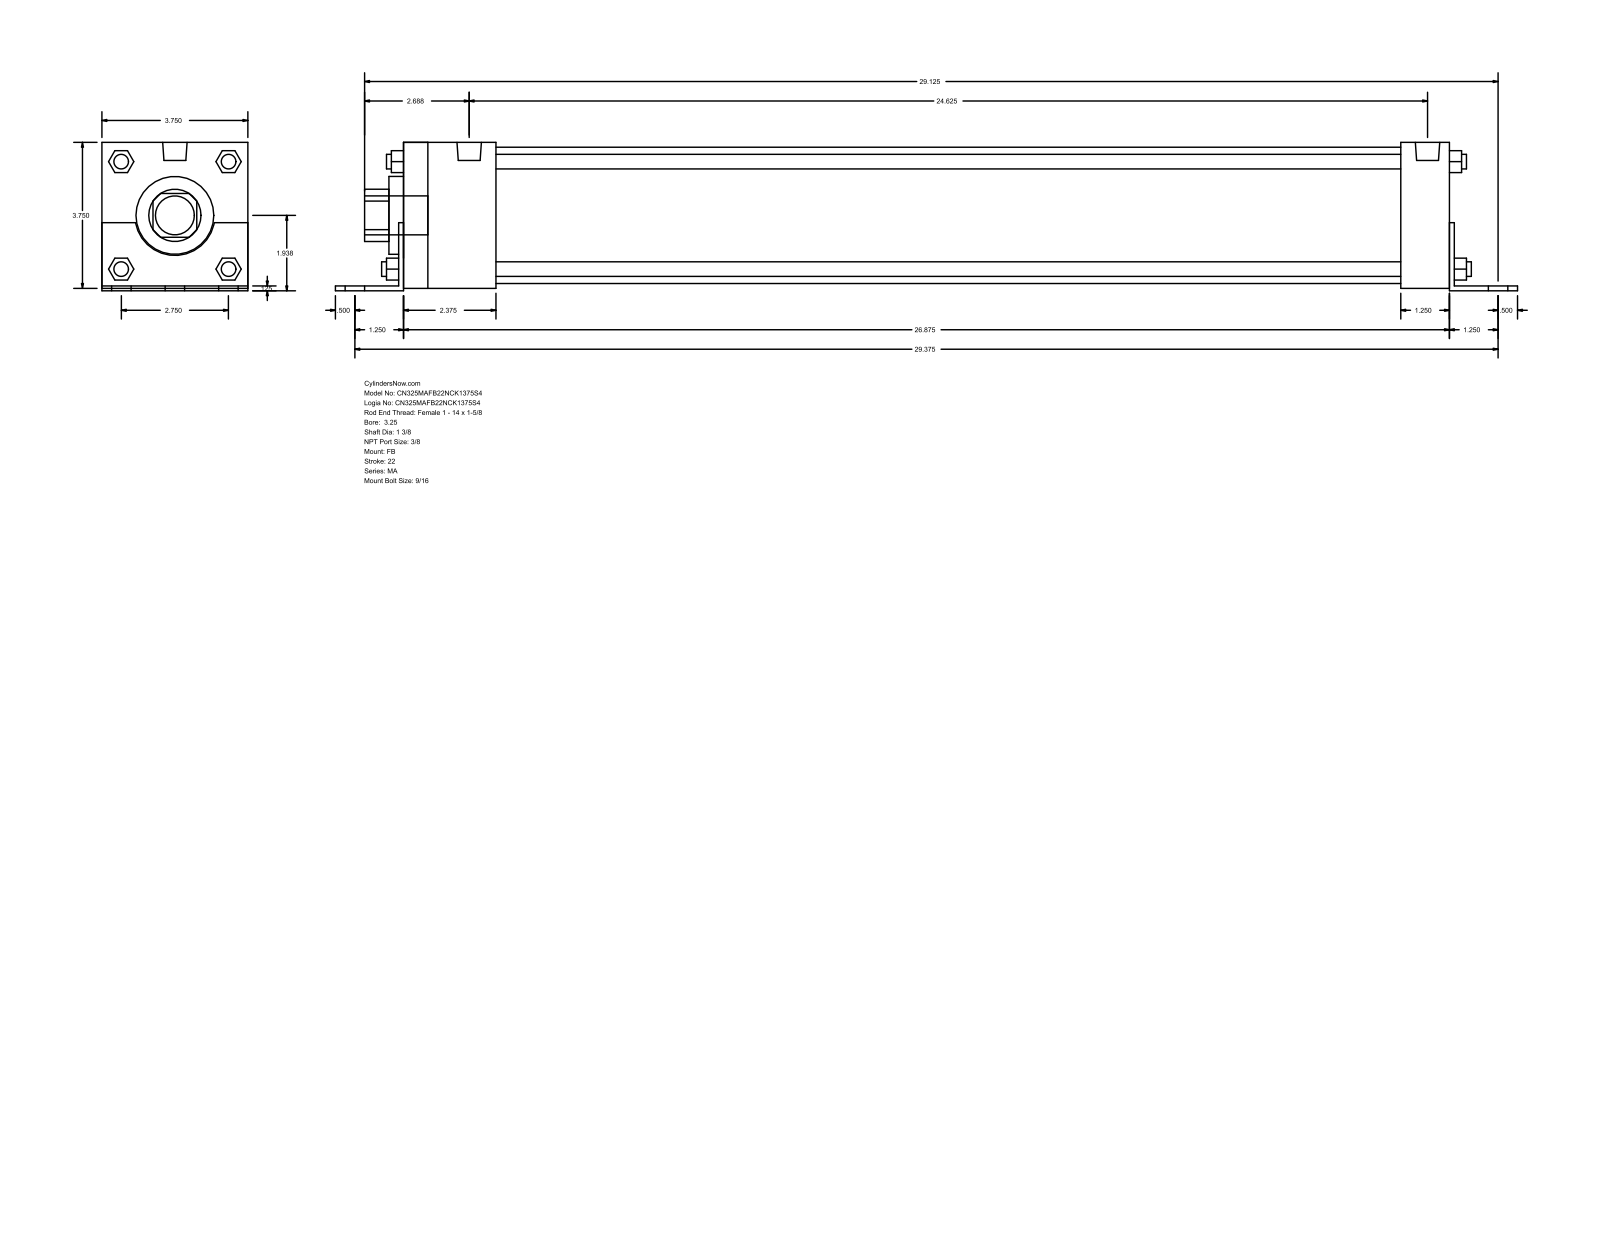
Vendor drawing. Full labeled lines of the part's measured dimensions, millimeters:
Part name (STEP PRODUCT): MA_FB__0325_1.375
STEP written by: GSSL Pune (CONFIG_CONTROL_DESIGN)
Units: millimetres
Bodies: 0 solids, 140 faces (105 planar, 35 cylindrical, 0 other)
Overall size (bounding box): 771.52 × 96.84 × 95.25
Round holes (diameter × count): ⌀34.92 ×1, ⌀50.8 ×1, ⌀88.9 ×1
Round bosses / shafts (diameter × count): ⌀14.29 ×6, ⌀11.11 ×4, ⌀9.53 ×4, ⌀15.93 ×2, ⌀25.4 ×1
Partial cylindrical surfaces — rounded edges, fillets, slot ends (radius × count): R17.06 ×1, R26.16 ×1
Main face-to-face distances: 95.24, 3.17, 1.59, 96.83, 1.58, 93.66, 3.18, 682.62, 685.8, 31.75
